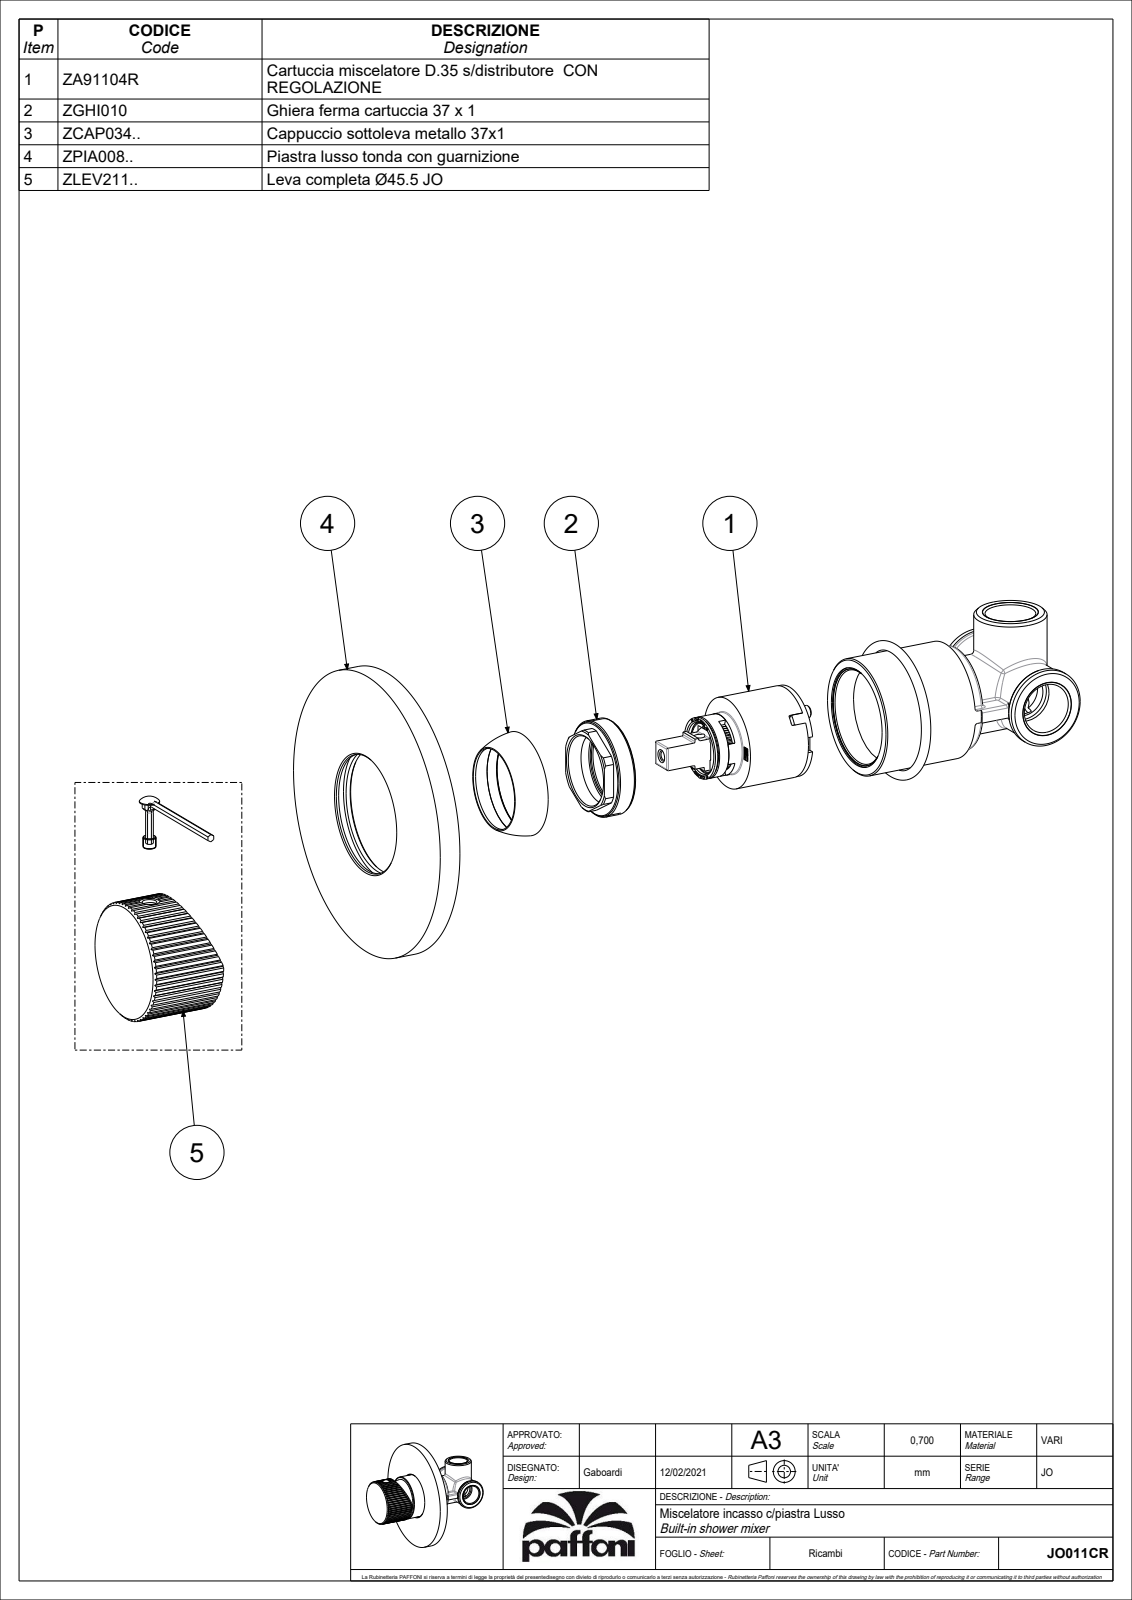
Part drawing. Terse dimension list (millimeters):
name: JO011CR
written by: CREO PARAMETRIC BY PTC INC, 2020044 (CONFIG_CONTROL_DESIGN)
unit: mm
bodies: 2 solids, 1082 faces (693 planar, 262 cylindrical, 127 other)
size: 110 × 110 × 54
volume: 60 885 mm³; area: 56 369 mm²
holes: 2× ⌀4, 1× ⌀3, 1× ⌀3.3, 1× ⌀5, 1× ⌀5.5, 1× ⌀10.5, 1× ⌀19.5, 1× ⌀19.9, 1× ⌀26.8, 1× ⌀29, 1× ⌀31, 1× ⌀32.4
bosses: 1× ⌀110, 1× ⌀54.6, 1× ⌀44.8, 1× ⌀35, 1× ⌀23.5, 1× ⌀23.4, 1× ⌀21.8, 1× ⌀16
rounds: 11× R0.15, 6× R0.5, 4× R0.3, 2× R1, 1× R4, 1× R7, 1× R9.3, 1× R10.85
face distances: 7, 50.6, 43.6, 1.5, 5.5, 9, 14.5, 16, 34.6, 6
hole spacings: 13
